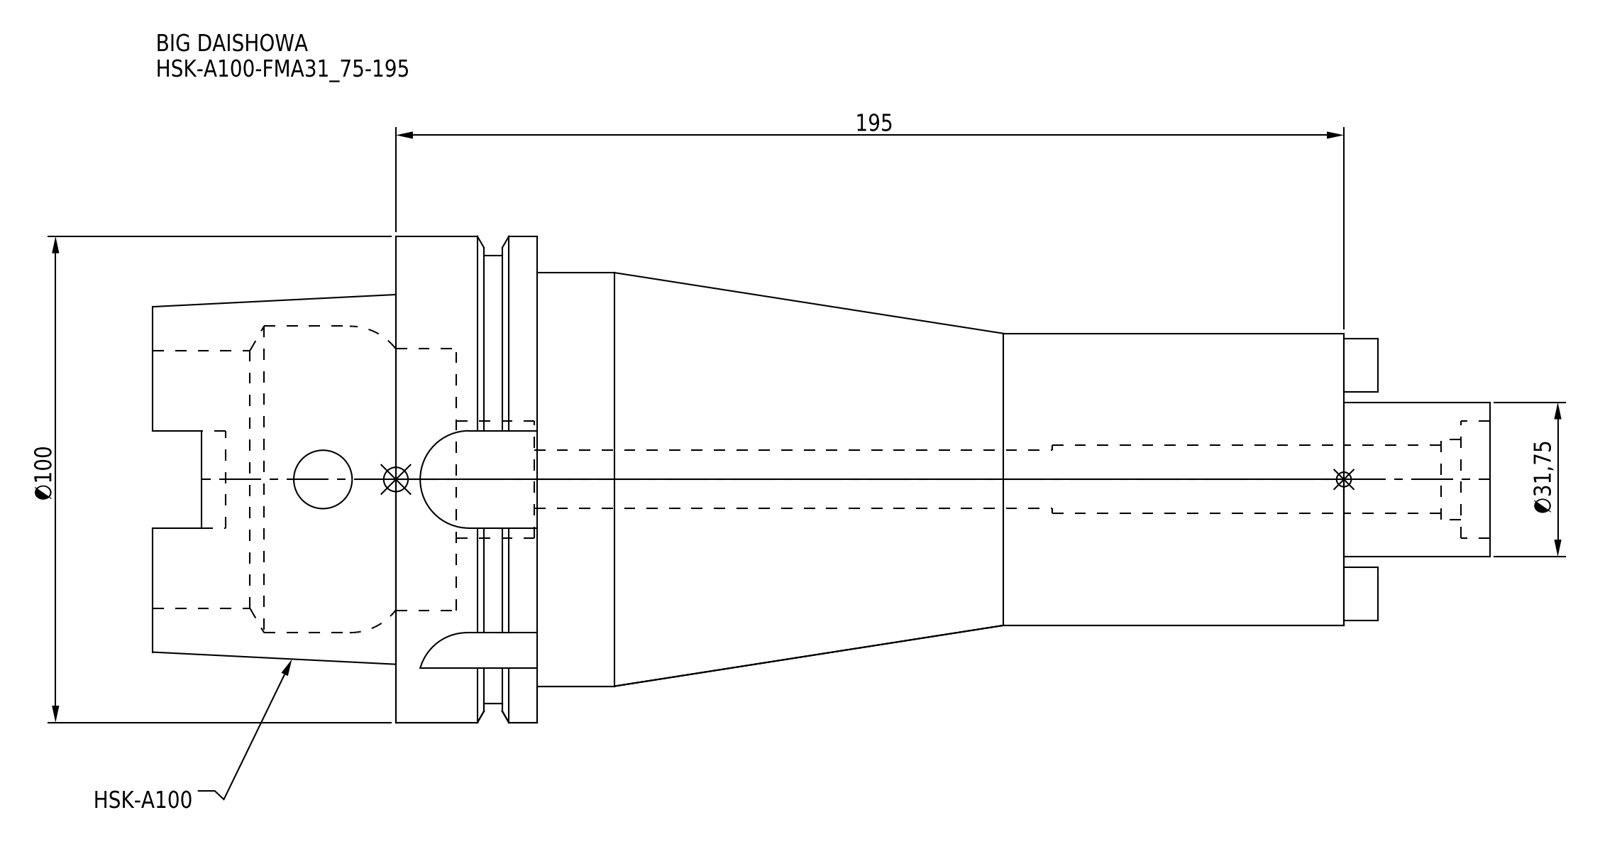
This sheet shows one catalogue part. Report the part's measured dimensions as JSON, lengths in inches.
{"part_name": "HSK-A100-FMA31_75-195", "step_written_by": "CREO PARAMETRIC BY PTC INC, 2016380 (AUTOMOTIVE_DESIGN)", "units": "inches", "bodies": {"solids": 1, "faces": 108, "planar": 46, "cylindrical": 46, "other": 16}, "overall_size": [10.827, 3.937, 3.937], "volume_in3": 53.31, "surface_area_in2": 146.8, "round_holes": [[0.472, 2], [0.551, 1], [0.65, 1], [0.945, 1], [2.087, 1], [2.118, 1], [2.48, 1]], "round_bosses_or_shafts": [[3.937, 1], [3.622, 1], [3.346, 1], [2.362, 1], [1.25, 1]], "partial_cylinders_radius": [[0.192, 4], [0.394, 4]], "face_to_face_distances": [1.142, 0.652, 0.49, 6.535, 7.187, 7.677, 9.646, 3.11, 2.459, 1.969]}
